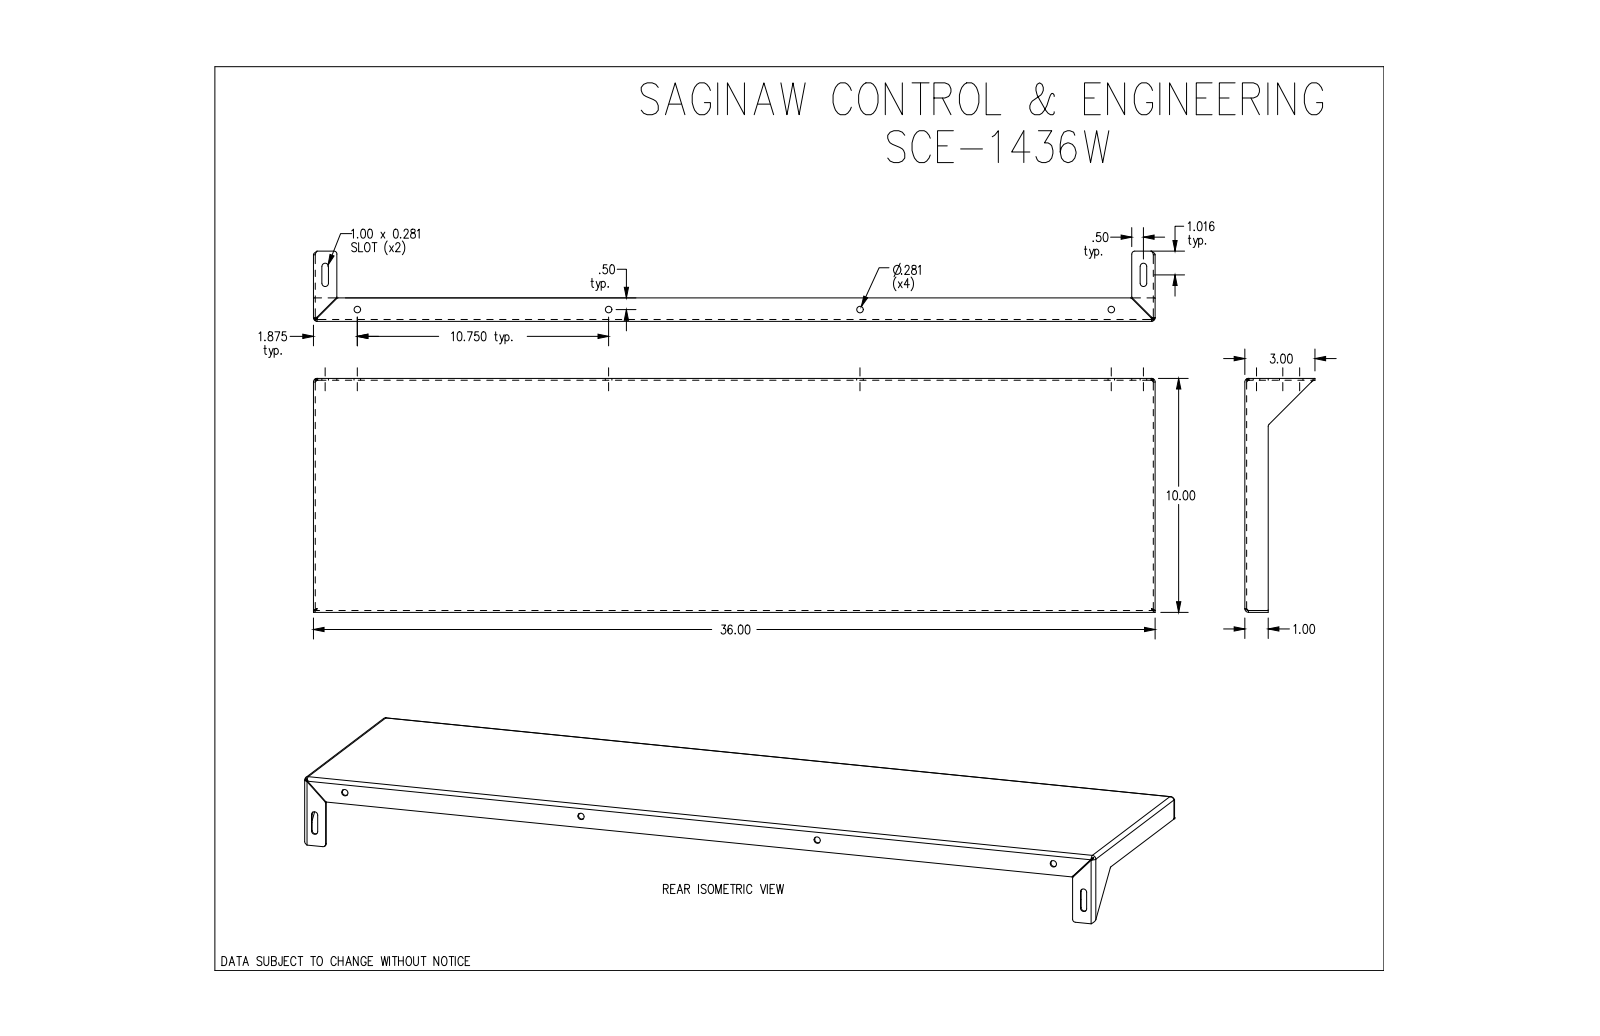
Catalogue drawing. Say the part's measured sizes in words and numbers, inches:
The part is named "SCE-1436W". Its 3-D file was written by "SolidWorks 2019 (AUTOMOTIVE_DESIGN)". It is 1 solid with 44 faces: 28 planar, 14 cylindrical and 2 other. Overall it measures 36 by 10 by 3 inches. Its volume is 22.54 cubic inches and its surface area 906.5 square inches. Round holes: 4 of diameter 0.281. Partial cylindrical surfaces (rounded edges, fillets, slot ends): 4 of radius 0.141, 2 of radius 0.106, 2 of radius 0.156, 1 of radius 0.125. The main face-to-face distances are 0.05, 9.95, 10, 9.9, 35.95, 36, 35.9, 0.95, 1, 9.94. The hole center spacings are 10.75, 10.75, 21.5, 21.5, 32.25.
